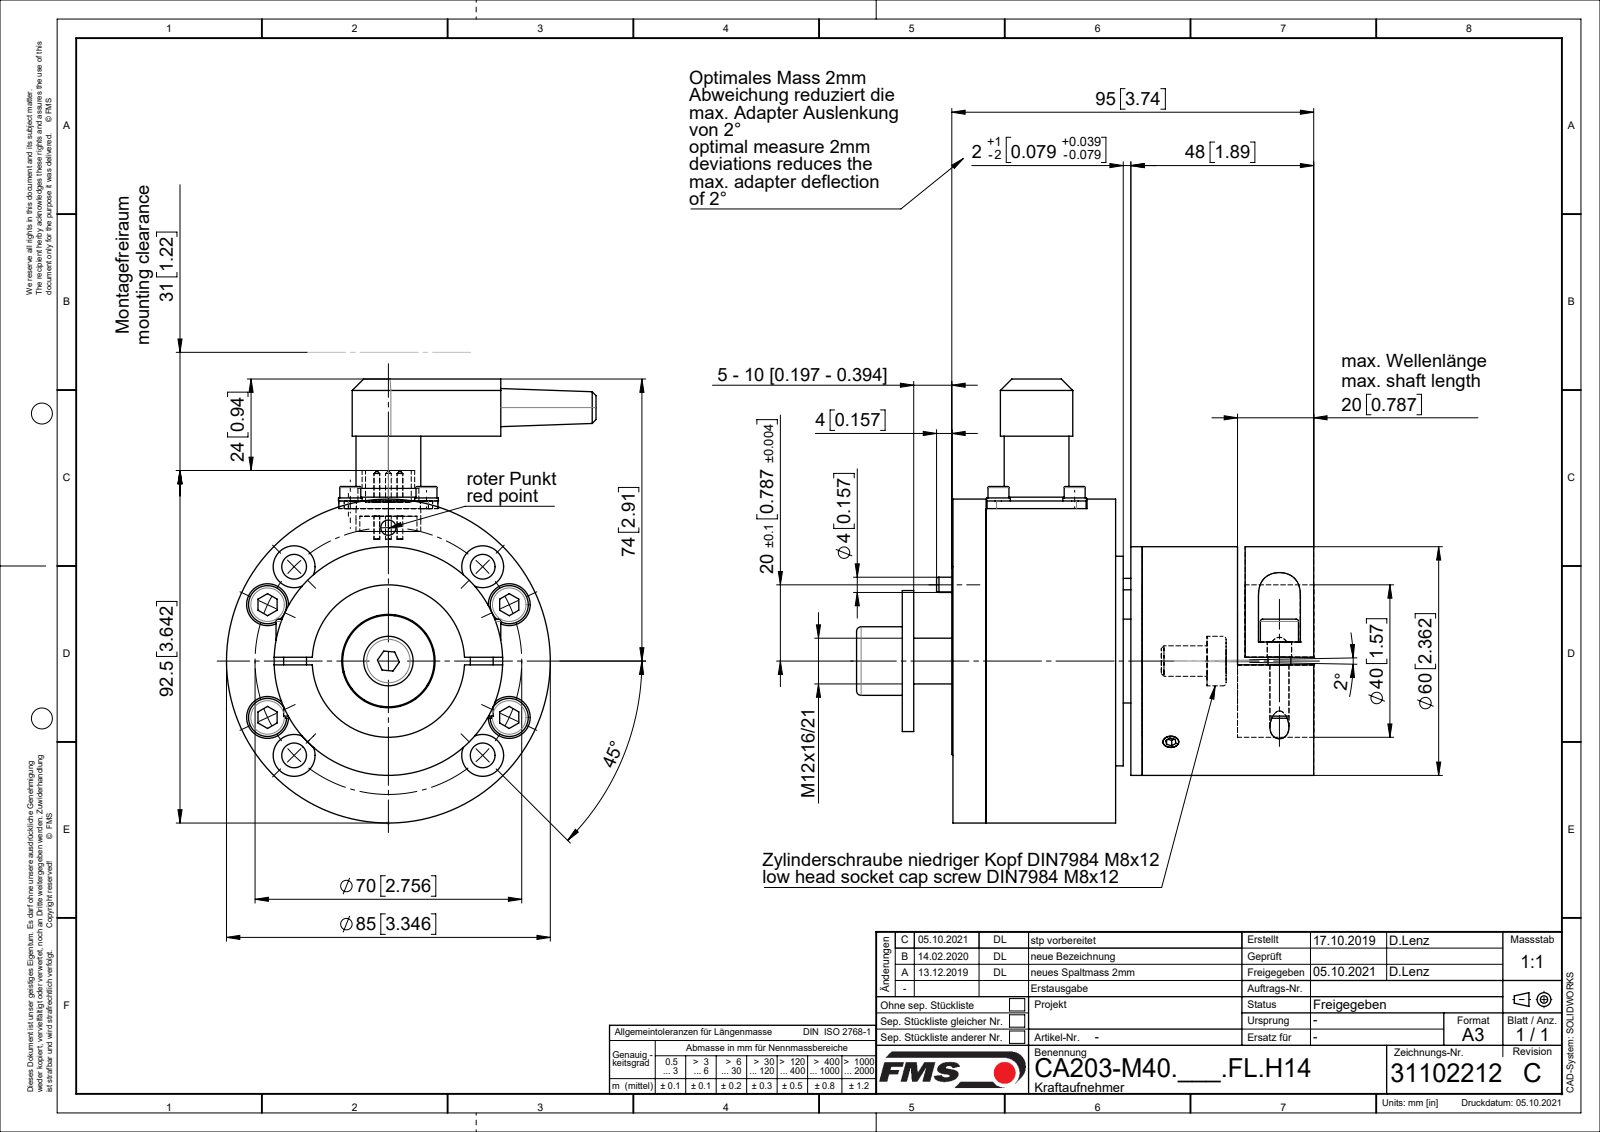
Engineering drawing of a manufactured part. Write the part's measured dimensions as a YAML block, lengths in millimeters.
part_name: "31102212_C; Zyl-Schr DIN912_M3x6; 070910-4_01; Zyl-Schr DIN912_M12x25 (+8 more)"
step_written_by: "SolidWorks 2018 (CONFIG_CONTROL_DESIGN)"
units: millimeters
bodies: {solids: 43, faces: 803, planar: 278, cylindrical: 333, other: 192}
overall_size: [120, 116.5, 97]
volume: 301293
surface_area: 113389
round_holes:
  - {diameter: 2.5, count: 8}
  - {diameter: 6.5, count: 8}
  - {diameter: 11, count: 8}
  - {diameter: 5, count: 6}
  - {diameter: 2, count: 5}
  - {diameter: 4, count: 5}
  - {diameter: 3.1, count: 4}
  - {diameter: 3.2, count: 4}
  - {diameter: 3.6, count: 4}
  - {diameter: 7, count: 4}
  - {diameter: 3, count: 2}
  - {diameter: 6.4, count: 2}
round_bosses_or_shafts:
  - {diameter: 3, count: 8}
  - {diameter: 6, count: 7}
  - {diameter: 10, count: 6}
  - {diameter: 1.5, count: 5}
  - {diameter: 6.2, count: 4}
  - {diameter: 5.7, count: 4}
  - {diameter: 5.5, count: 4}
  - {diameter: 85, count: 1}
partial_cylinders:
  - {radius: 2.5, count: 4}
  - {radius: 5, count: 2}
  - {radius: 5.5, count: 2}
  - {radius: 9.5, count: 1}
face_to_face_distances: [2, 10, 41, 30, 3, 45, 60, 22, 34, 15]
hole_center_spacings: [35, 20, 24.78, 25.2, 32.8, 51.14, 56.46, 6]
